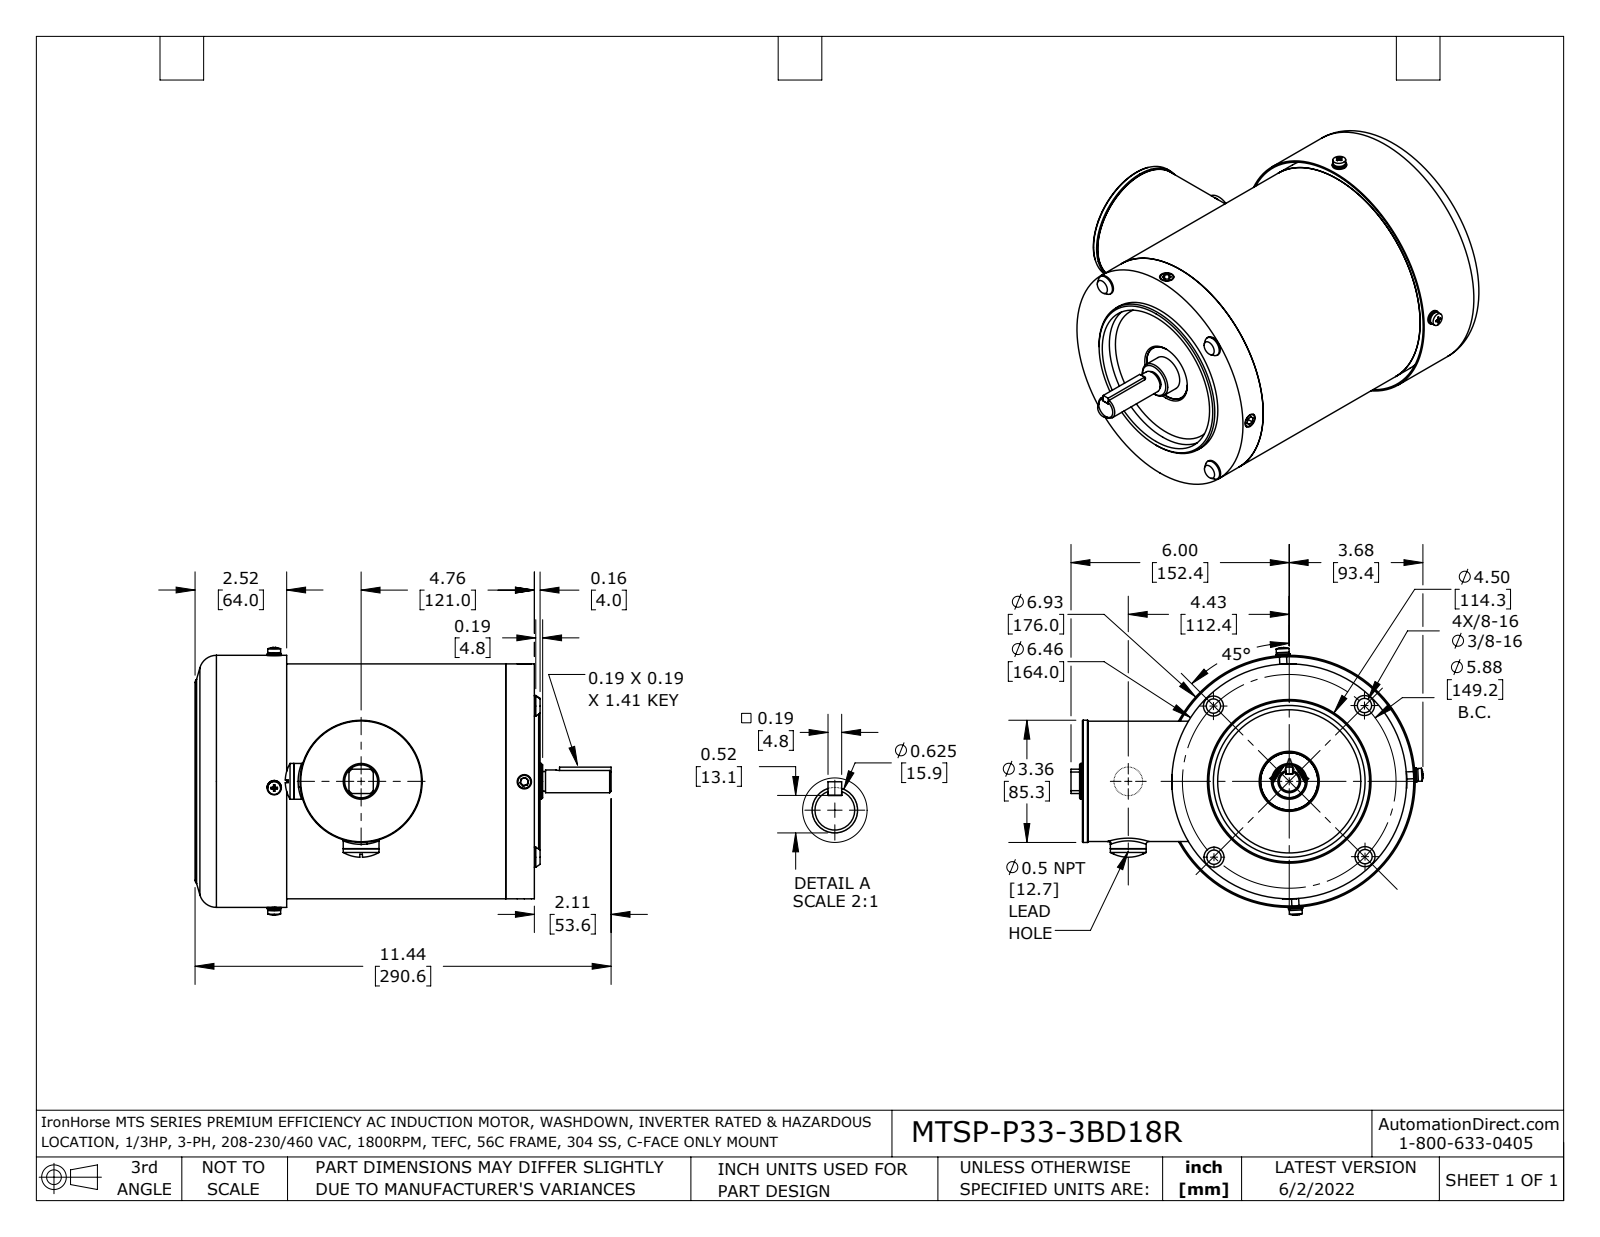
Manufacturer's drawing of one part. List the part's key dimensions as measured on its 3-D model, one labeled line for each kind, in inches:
Part name (STEP PRODUCT): MTSP-P33-3BD18R
STEP written by: SolidWorks 2021 (AUTOMOTIVE_DESIGN)
Units: inches
Bodies: 39 solids, 1357 faces (386 planar, 484 cylindrical, 487 other)
Overall size (bounding box): 11.441 × 9.68 × 7.357
Volume: 49.96 in³ · Surface area: 856.9 in²
Round holes (diameter × count): ⌀0.165 ×10, ⌀0.217 ×8, ⌀0.213 ×4, ⌀0.236 ×4, ⌀0.335 ×4, ⌀0.354 ×4, ⌀0.118 ×2, ⌀0.472 ×2, ⌀0.656 ×2, ⌀1.378 ×2, ⌀0.984 ×1, ⌀1.024 ×1
Round bosses / shafts (diameter × count): ⌀0.394 ×8, ⌀0.551 ×4, ⌀0.354 ×4, ⌀0.331 ×4, ⌀0.315 ×4, ⌀0.197 ×4, ⌀0.984 ×3, ⌀0.787 ×2
Partial cylindrical surfaces — rounded edges, fillets, slot ends (radius × count): R0.128 ×36, R0.039 ×35, R0.079 ×32, R0.012 ×16, R0.118 ×9, R0.236 ×8, R0.217 ×4, R0.394 ×4
Main face-to-face distances: 0.118, 7.323, 0.236, 0.039, 7.087, 7.205, 7.441, 1.949, 1.831, 9.272
Hole centre spacings: 2.937, 4.154, 0.133, 1.181, 1.312, 2.992, 3.163, 3.234
